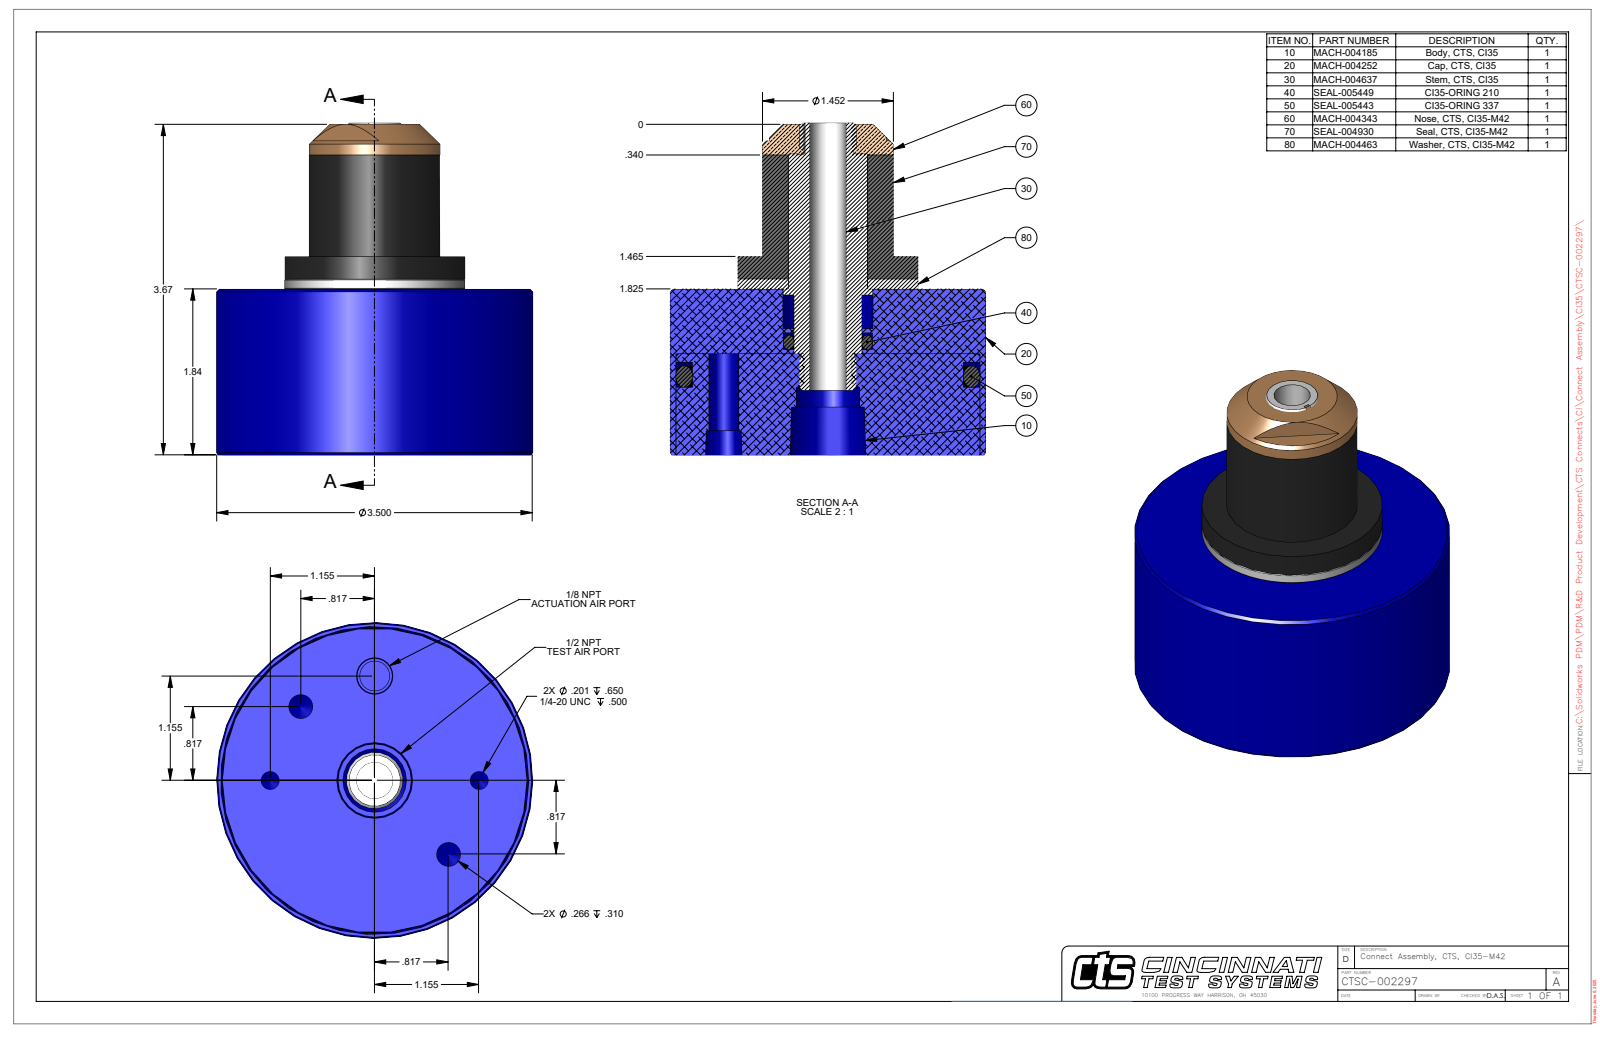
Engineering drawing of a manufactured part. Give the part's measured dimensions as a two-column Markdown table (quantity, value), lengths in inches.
| quantity | value |
| --- | --- |
| part name | CTSC-002297 |
| STEP written by | SolidWorks 2023 (AUTOMOTIVE_DESIGN) |
| units | inches |
| bodies | 1 solid, 77 faces (21 planar, 29 cylindrical, 27 other) |
| overall size | 3.68 × 3.5 × 3.5 |
| volume | 20.21 in³ |
| surface area | 70.28 in² |
| round holes (diameter × count) | 0.201 × 2, 0.266 × 2, 0.332 × 1, 0.406 × 1, 0.703 × 1, 3.373 × 1 |
| round bosses / shafts (diameter × count) | 3.5 × 1, 3.365 × 1, 1.998 × 1, 1.998 × 1, 1.452 × 1, 1.452 × 1 |
| partial cylindrical surfaces (radius × count) | 0.266 × 1 |
| main face-to-face distances | 1.84, 2.2, 0.36, 3.665, 1.825, 1.465, 0.719, 1.121, 1.481, 2.946 |
| hole center spacings | 0.884, 1.155, 2.134, 1.155, 1.633, 2.309, 2.31 |
